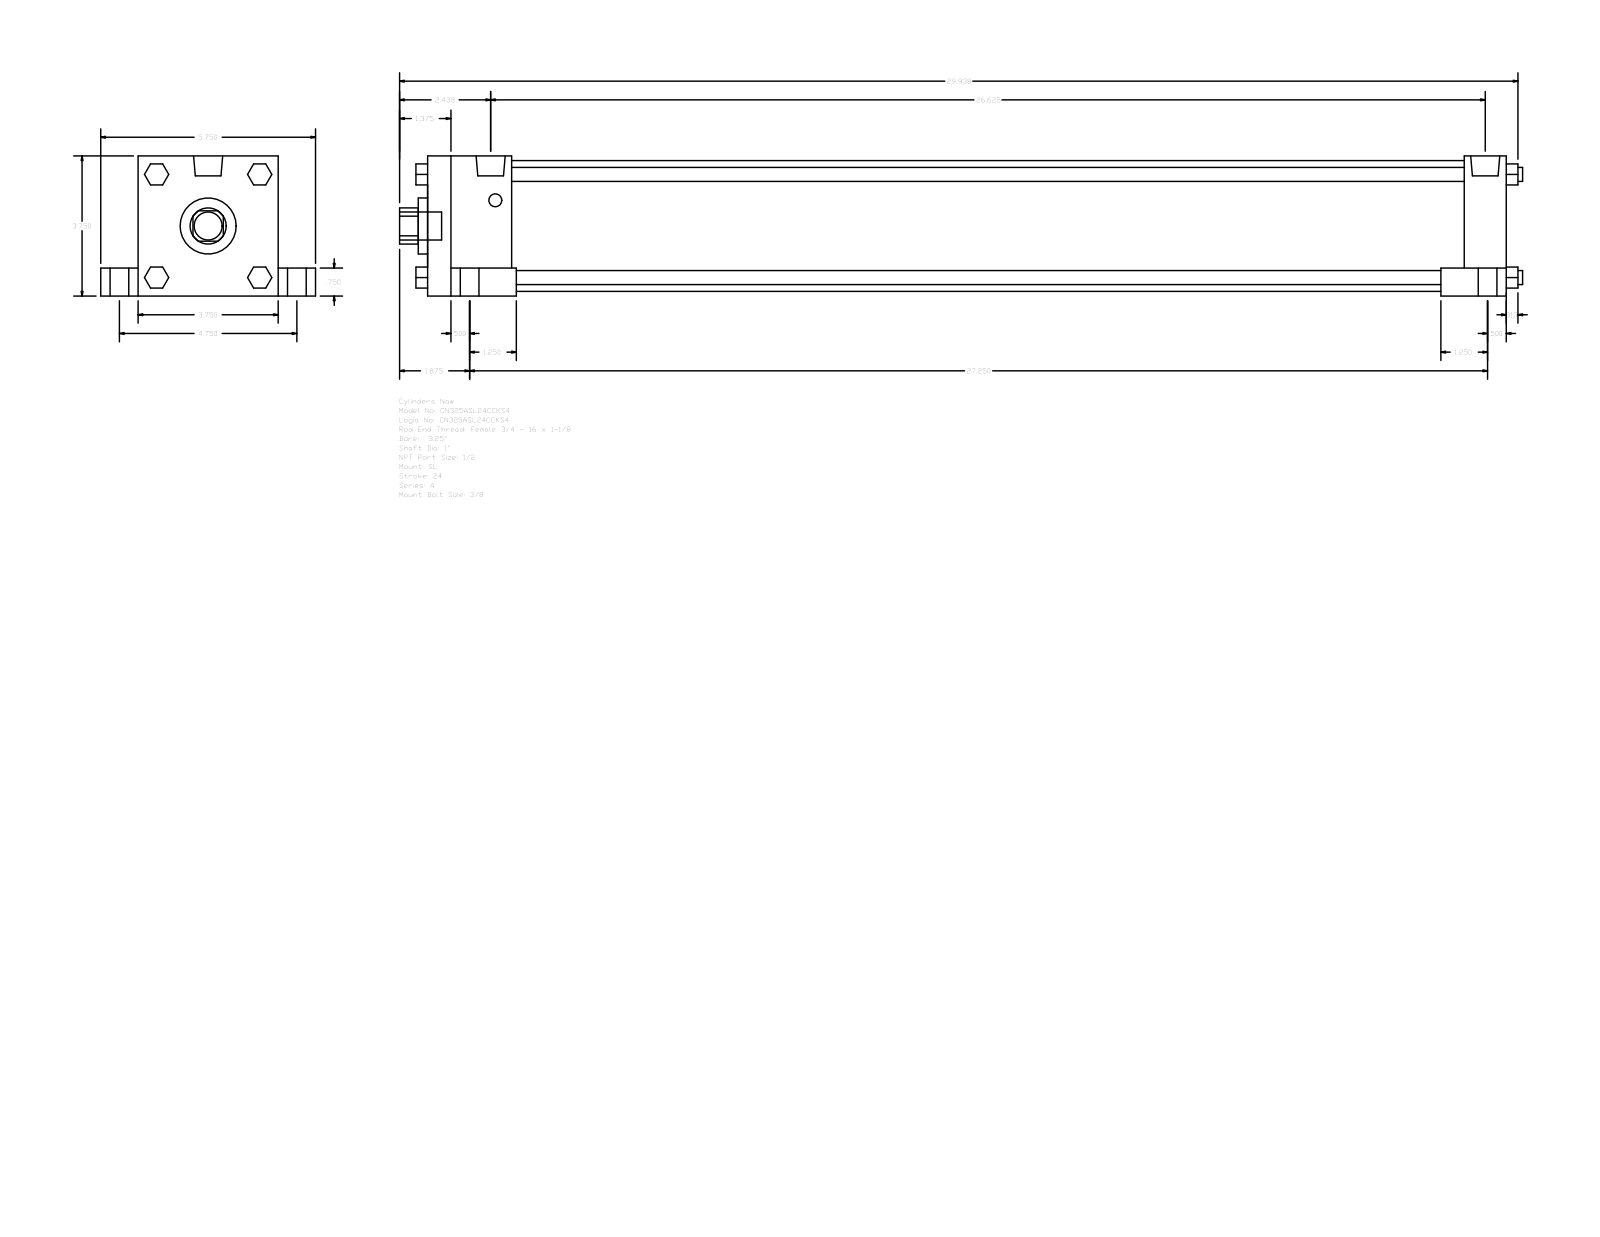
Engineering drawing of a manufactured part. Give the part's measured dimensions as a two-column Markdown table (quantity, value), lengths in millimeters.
| quantity | value |
| --- | --- |
| part name | A_SL__0325_1 |
| STEP written by | GSSL Pune (CONFIG_CONTROL_DESIGN) |
| units | millimeters |
| bodies | 0 solids, 150 faces (114 planar, 36 cylindrical, 0 other) |
| overall size | 763.59 × 146.05 × 95.25 |
| round holes (diameter × count) | 25.4 × 1, 38.1 × 1, 88.9 × 1 |
| round bosses / shafts (diameter × count) | 19.05 × 5, 12.7 × 4, 9.53 × 4, 8.73 × 4, 19.77 × 2 |
| partial cylindrical surfaces (radius × count) | 12.29 × 1 |
| main face-to-face distances | 95.24, 733.43, 19.05, 25.41, 120.65, 76.19, 57.15, 704.85, 647.7, 676.28 |
